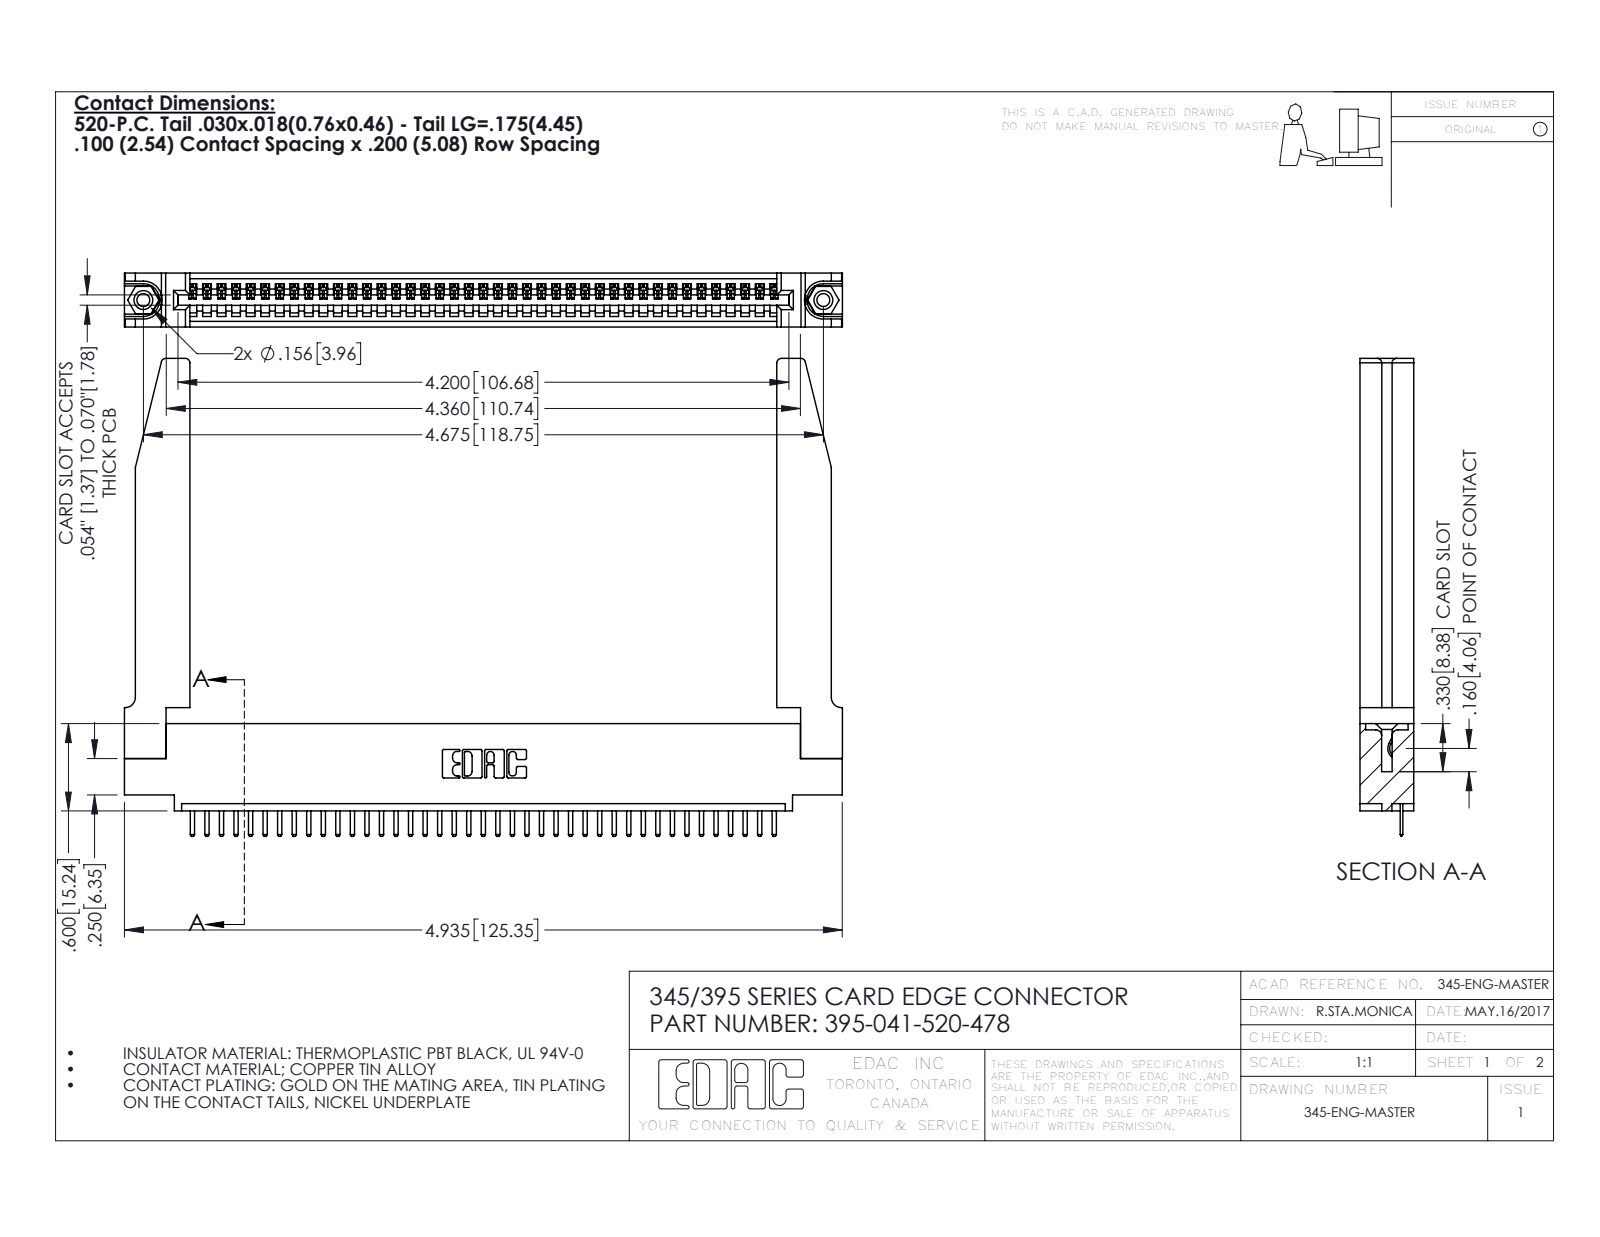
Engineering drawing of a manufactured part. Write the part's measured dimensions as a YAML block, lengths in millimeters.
part_name: "345 Part_0.110 Offset - 0.156 Dia-TH; 395-041-520-478; 345-250-001_345-250-001-102; 345-292-001_345-293-120 (+1 more)"
step_written_by: "SolidWorks 2016 (CONFIG_CONTROL_DESIGN)"
units: millimeters
bodies: {solids: 46, faces: 2906, planar: 1948, cylindrical: 906, other: 52}
overall_size: [125.4, 83.4, 9.4]
volume: 19480
surface_area: 22090
round_holes:
  - {diameter: 2.3, count: 2}
  - {diameter: 3.2, count: 2}
  - {diameter: 4, count: 2}
  - {diameter: 1.6, count: 1}
round_bosses_or_shafts:
  - {diameter: 3.9, count: 2}
partial_cylinders:
  - {radius: 0.3, count: 84}
  - {radius: 0.2, count: 82}
  - {radius: 0.3, count: 22}
  - {radius: 0.8, count: 8}
  - {radius: 0.2, count: 6}
  - {radius: 0.8, count: 6}
  - {radius: 0.7, count: 3}
  - {radius: 0.8, count: 2}
face_to_face_distances: [9.4, 1.8, 7.6, 5.1, 2.5, 6.9, 0.6, 5.7, 3.8, 3.8]
hole_center_spacings: [6.9, 112.8, 118.7]
